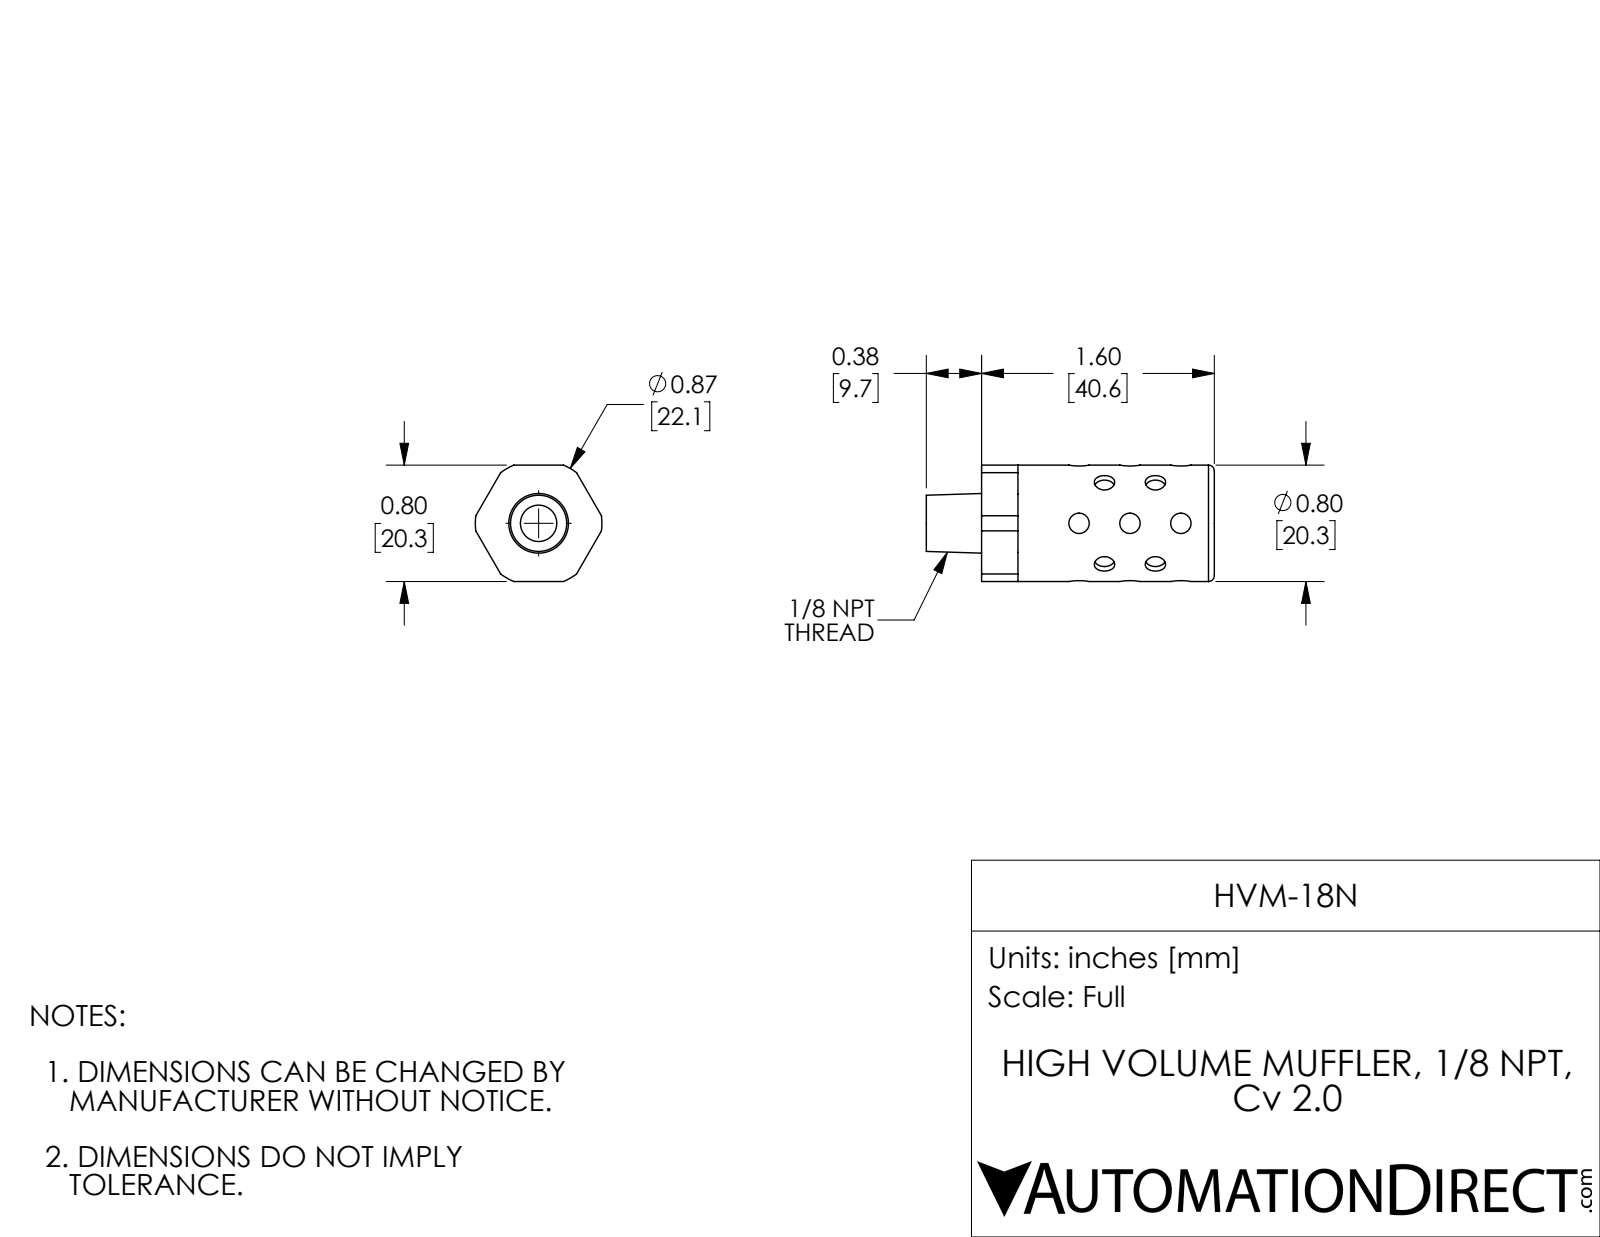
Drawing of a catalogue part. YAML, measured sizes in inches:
part_name: "HVM-18N"
step_written_by: "SolidWorks 2017 (AUTOMOTIVE_DESIGN)"
units: inches
bodies: {solids: 1, faces: 91, planar: 36, cylindrical: 51, other: 4}
overall_size: [1.98, 0.87, 0.8]
volume: 0.762
surface_area: 7.341
round_holes:
  - {diameter: 0.14, count: 10}
  - {diameter: 0.25, count: 1}
round_bosses_or_shafts:
  - {diameter: 0.8, count: 1}
partial_cylinders:
  - {radius: 0.435, count: 1}
face_to_face_distances: [1.6, 0.8, 0.7, 0.25, 1.35, 0.05, 0.75, 0.38, 1.98, 1.73]
hole_center_spacings: [0.35, 0.7]
